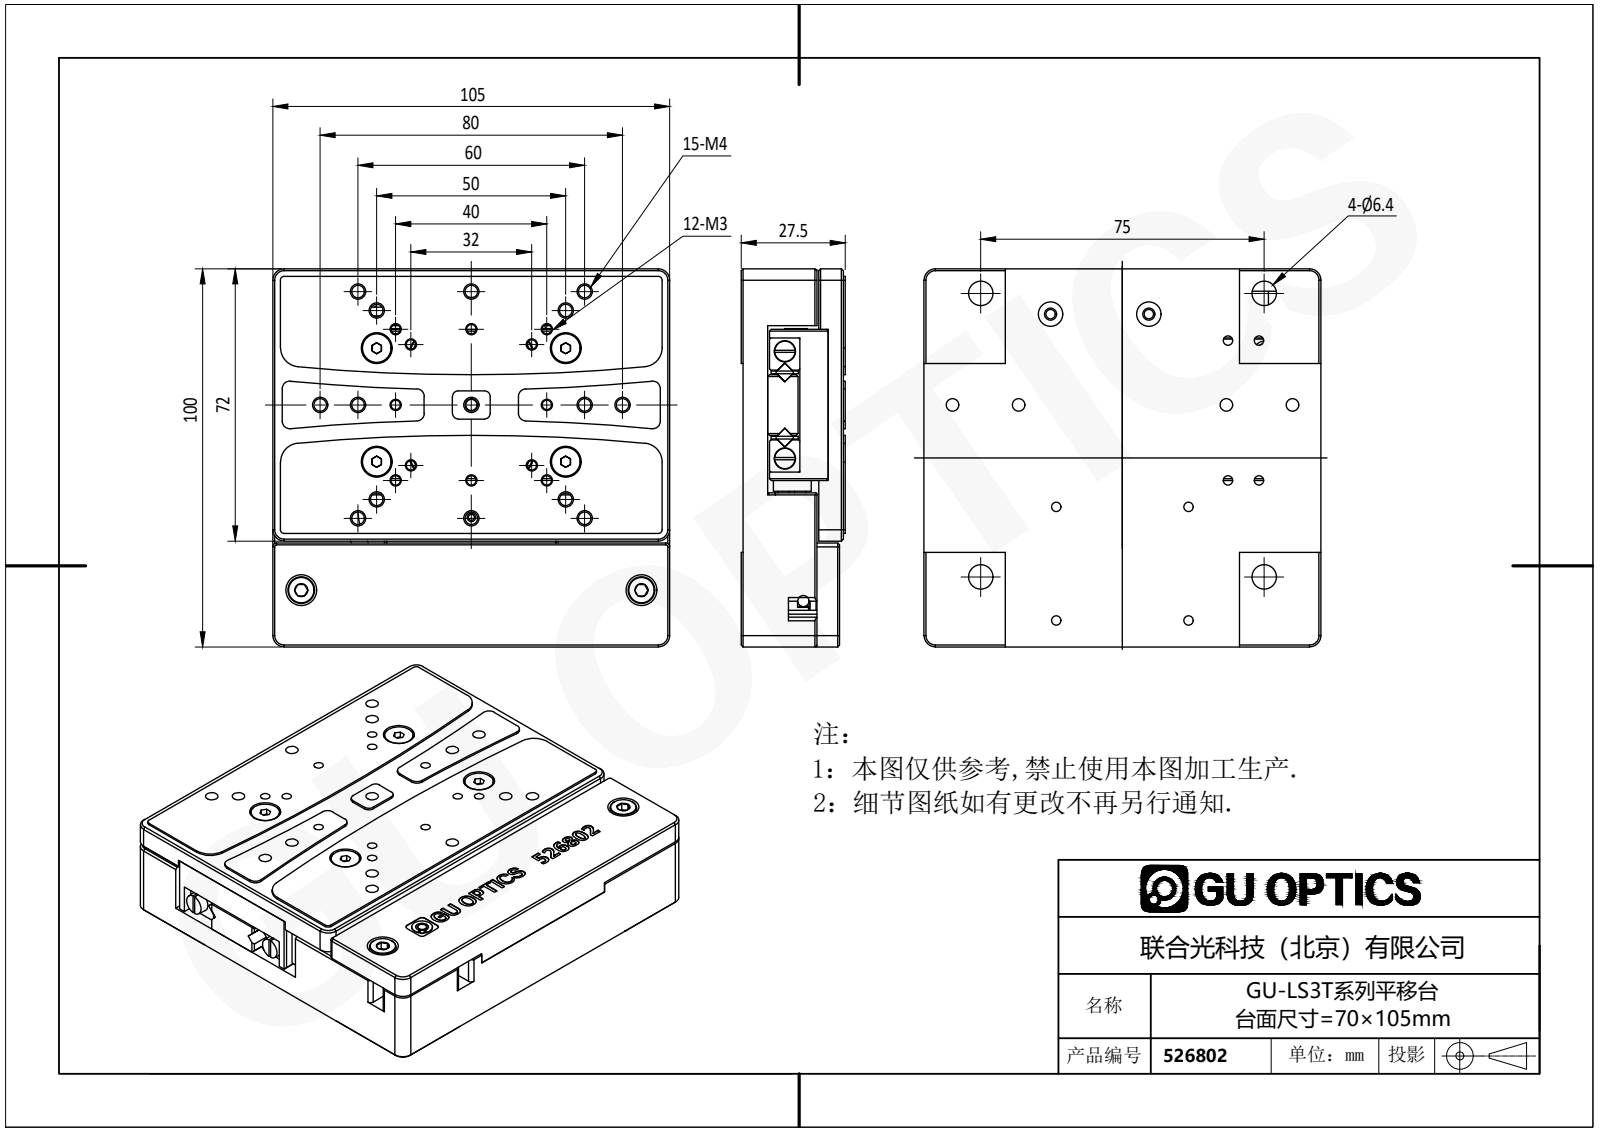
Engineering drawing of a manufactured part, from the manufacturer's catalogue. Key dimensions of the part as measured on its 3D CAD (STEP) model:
Part name (STEP PRODUCT): GU-LS3T系列平移台 台面尺寸=70×105mm
STEP written by: SolidWorks 2019 (AUTOMOTIVE_DESIGN)
Units: millimetres
Bodies: 0 solids, 1293 faces (579 planar, 415 cylindrical, 299 other)
Overall size (bounding box): 105 × 100 × 27.5
Round holes (diameter × count): ⌀3 ×21, ⌀3.3 ×21, ⌀4 ×21, ⌀2.5 ×20, ⌀7.5 ×12, ⌀5.4 ×8, ⌀4.3 ×6, ⌀8.2 ×6, ⌀1.57 ×4, ⌀3.24 ×4, ⌀4.5 ×4, ⌀6.4 ×4
Round bosses / shafts (diameter × count): ⌀4 ×12, ⌀7 ×10, ⌀7.53 ×4, ⌀3.24 ×2
Partial cylindrical surfaces — rounded edges, fillets, slot ends (radius × count): R1 ×17, R2 ×13, R3 ×12, R1.5 ×5, R2.6 ×4, R5 ×4, R7.9 ×3, R12.1 ×3
Main face-to-face distances: 0.5, 6.5, 16, 7, 7.5, 20, 4.5, 20.5, 22.5, 3
Hole centre spacings: 25, 50, 75, 37.84, 12.53, 16.06, 17.37, 20.66
